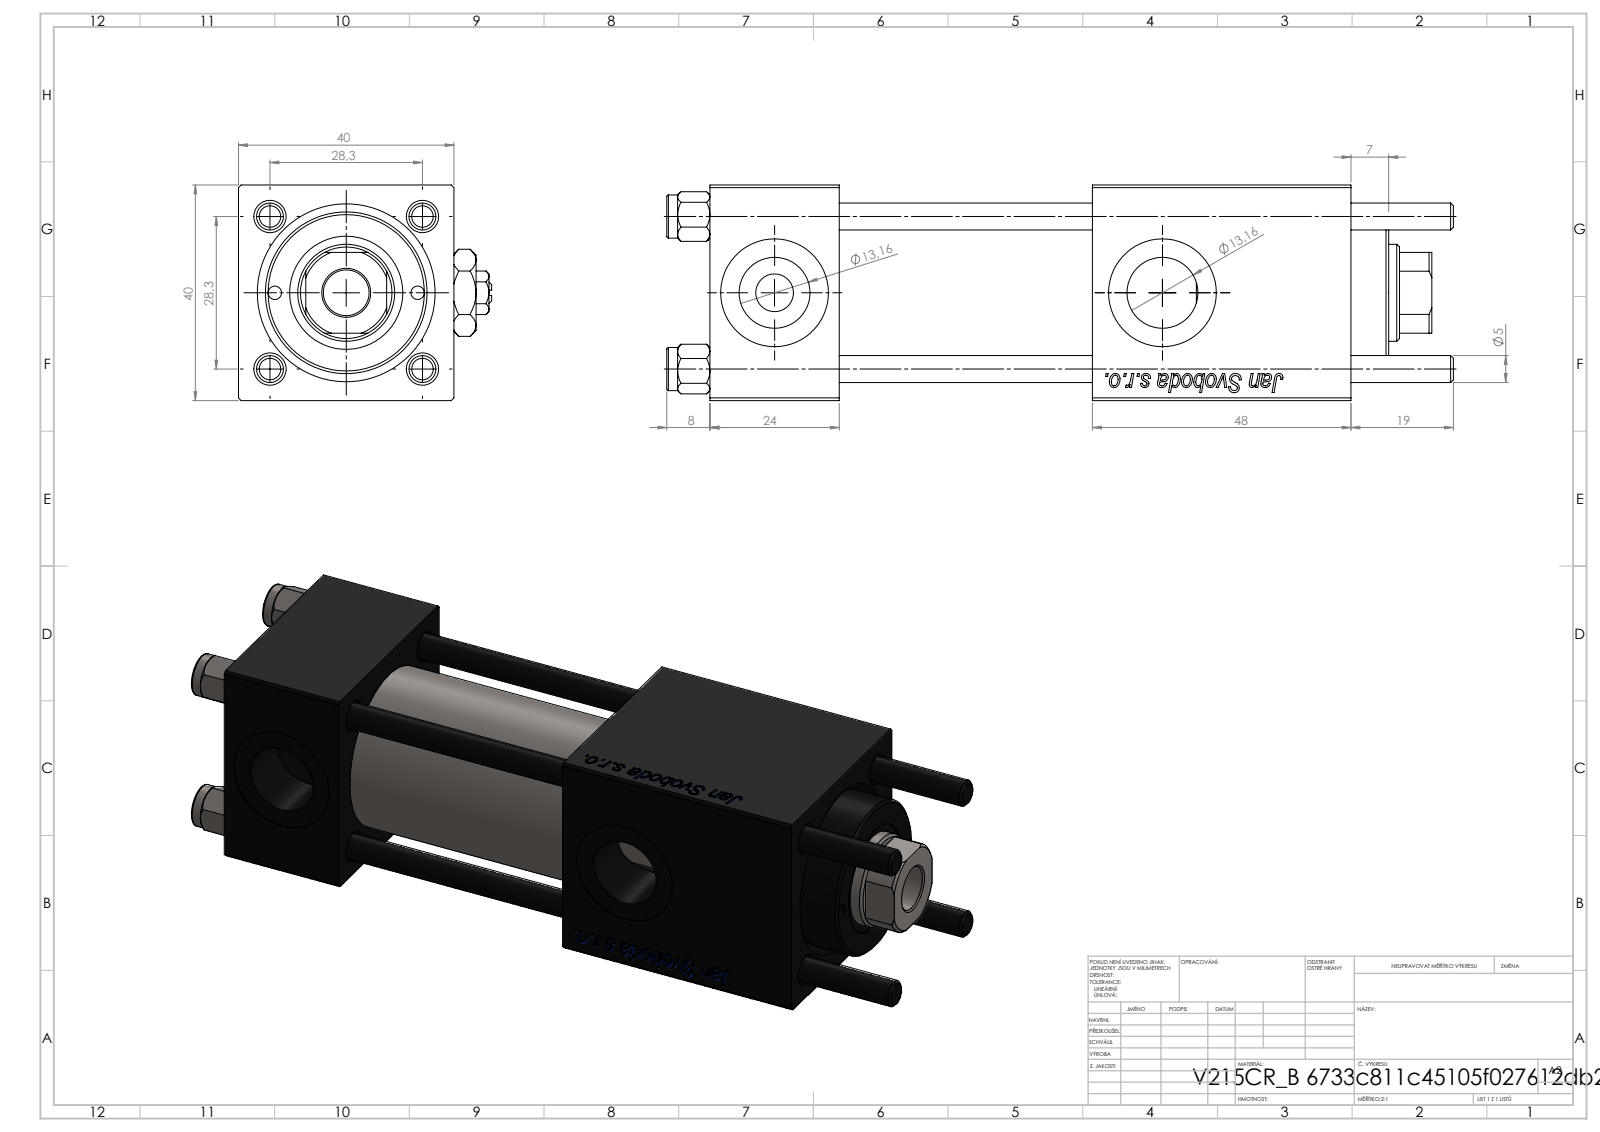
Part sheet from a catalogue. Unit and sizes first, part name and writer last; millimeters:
Units: millimetres
Overall size (bounding box): 146 × 47 × 40
Round holes (diameter × count): ⌀5 ×4, ⌀20 ×3, ⌀2.5 ×2, ⌀7 ×2, ⌀13.16 ×2, ⌀8.5 ×1, ⌀18 ×1, ⌀21 ×1, ⌀25 ×1, ⌀30 ×1
Round bosses / shafts (diameter × count): ⌀8 ×4, ⌀31 ×1
Partial cylindrical surfaces — rounded edges, fillets, slot ends (radius × count): R8.5 ×1
Main face-to-face distances: 40, 24, 39.8, 47, 71, 90.3, 66.3, 19.3, 119, 95
Hole centre spacings: 14.18, 20.01, 28.3, 30.84, 13.25, 40.02, 26.5, 72
Volume: 150 970 mm³ · Surface area: 62 850 mm²
Bodies: 13 solids, 1259 faces (477 planar, 92 cylindrical, 690 other)
Part name (STEP PRODUCT): V215_VC_A; Zatka_pro_OIL_PORT; V215CR_VCP_B; V215CR_B_TYCINKA (+2 more)
STEP written by: SolidWorks 2019 (CONFIG_CONTROL_DESIGN)
